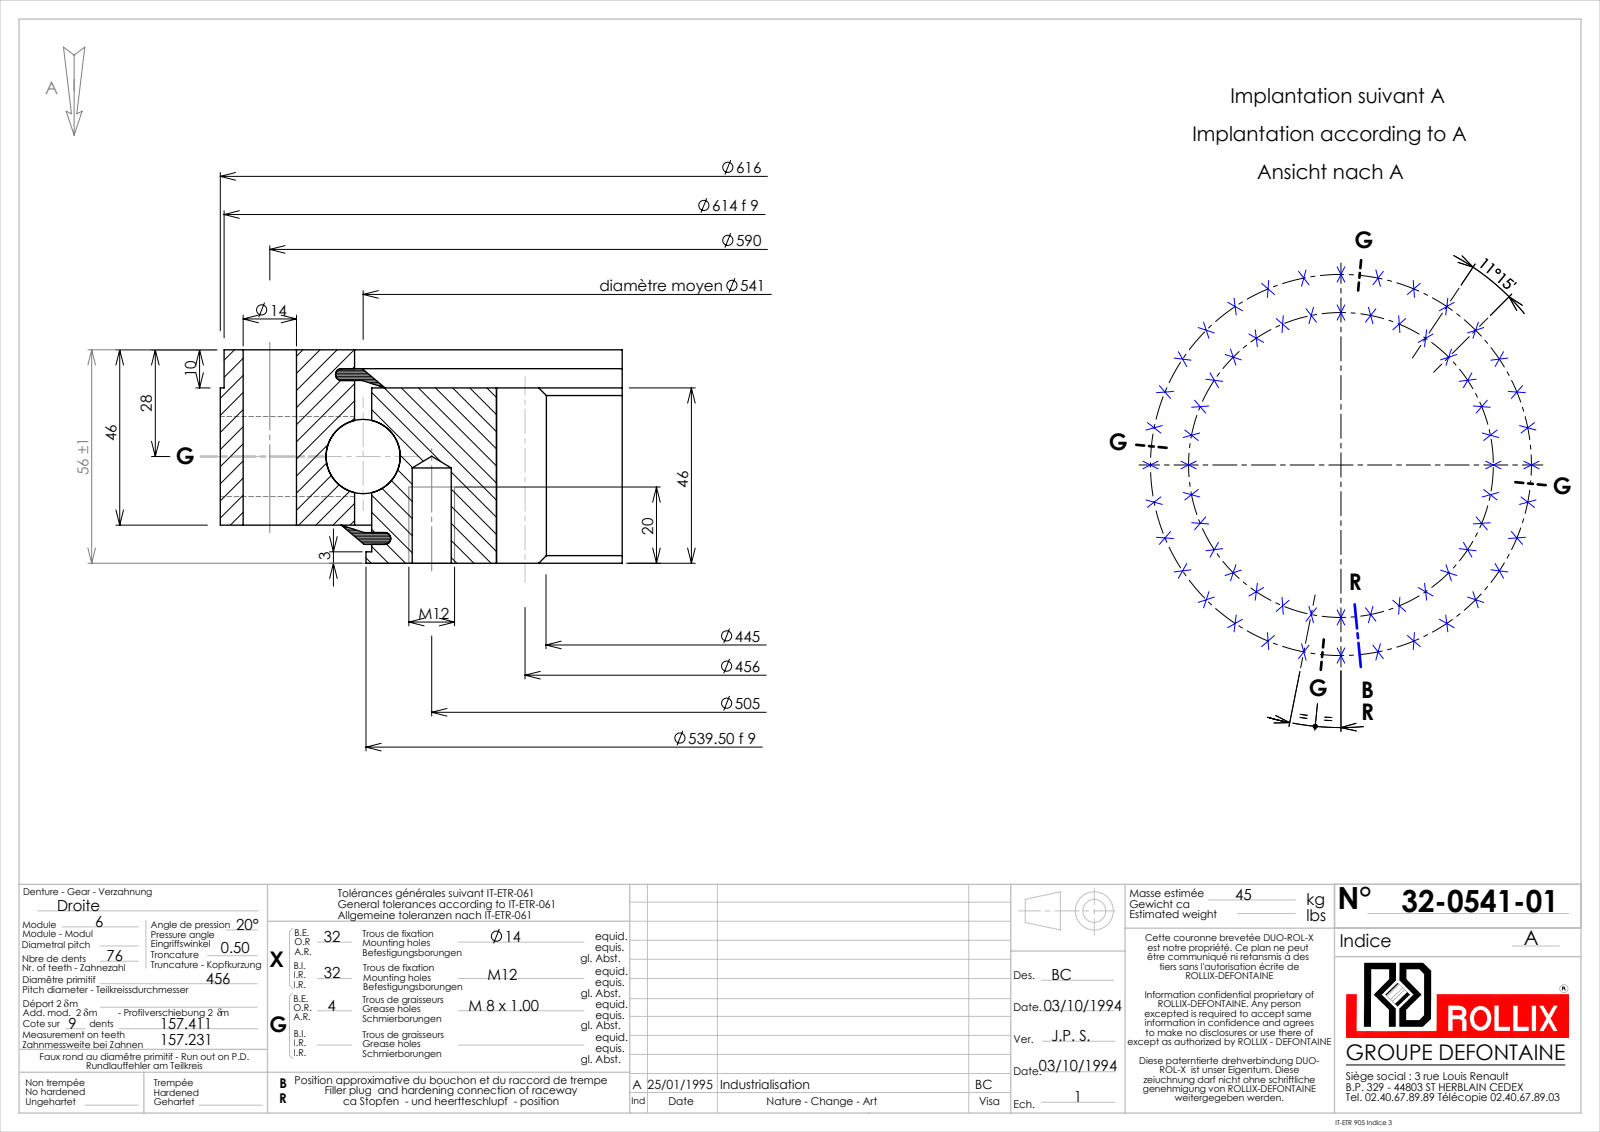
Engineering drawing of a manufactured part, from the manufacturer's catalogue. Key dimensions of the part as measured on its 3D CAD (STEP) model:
Part name (STEP PRODUCT): 32-0541-01
STEP written by: SolidWorks 2016 (CONFIG_CONTROL_DESIGN)
Units: millimetres
Bodies: 9 solids, 805 faces (206 planar, 315 cylindrical, 284 other)
Overall size (bounding box): 632.55 × 632.55 × 56
Volume: 5 194 000 mm³ · Surface area: 871 578 mm²
Round holes (diameter × count): ⌀10.25 ×32, ⌀14 ×32, ⌀7 ×4, ⌀545.5 ×1
Round bosses / shafts (diameter × count): ⌀8 ×4, ⌀616 ×1, ⌀614 ×1, ⌀539.5 ×1, ⌀536.5 ×1
Partial cylindrical surfaces — rounded edges, fillets, slot ends (radius × count): R222.5 ×1, R235.5 ×1
Main face-to-face distances: 46, 10, 36, 56, 1.95, 5.05, 43, 8.05, 47.95, 37.95
Hole centre spacings: 390.37, 445.37, 98.52, 357.09, 419.89, 466.56, 49.5, 238.06
